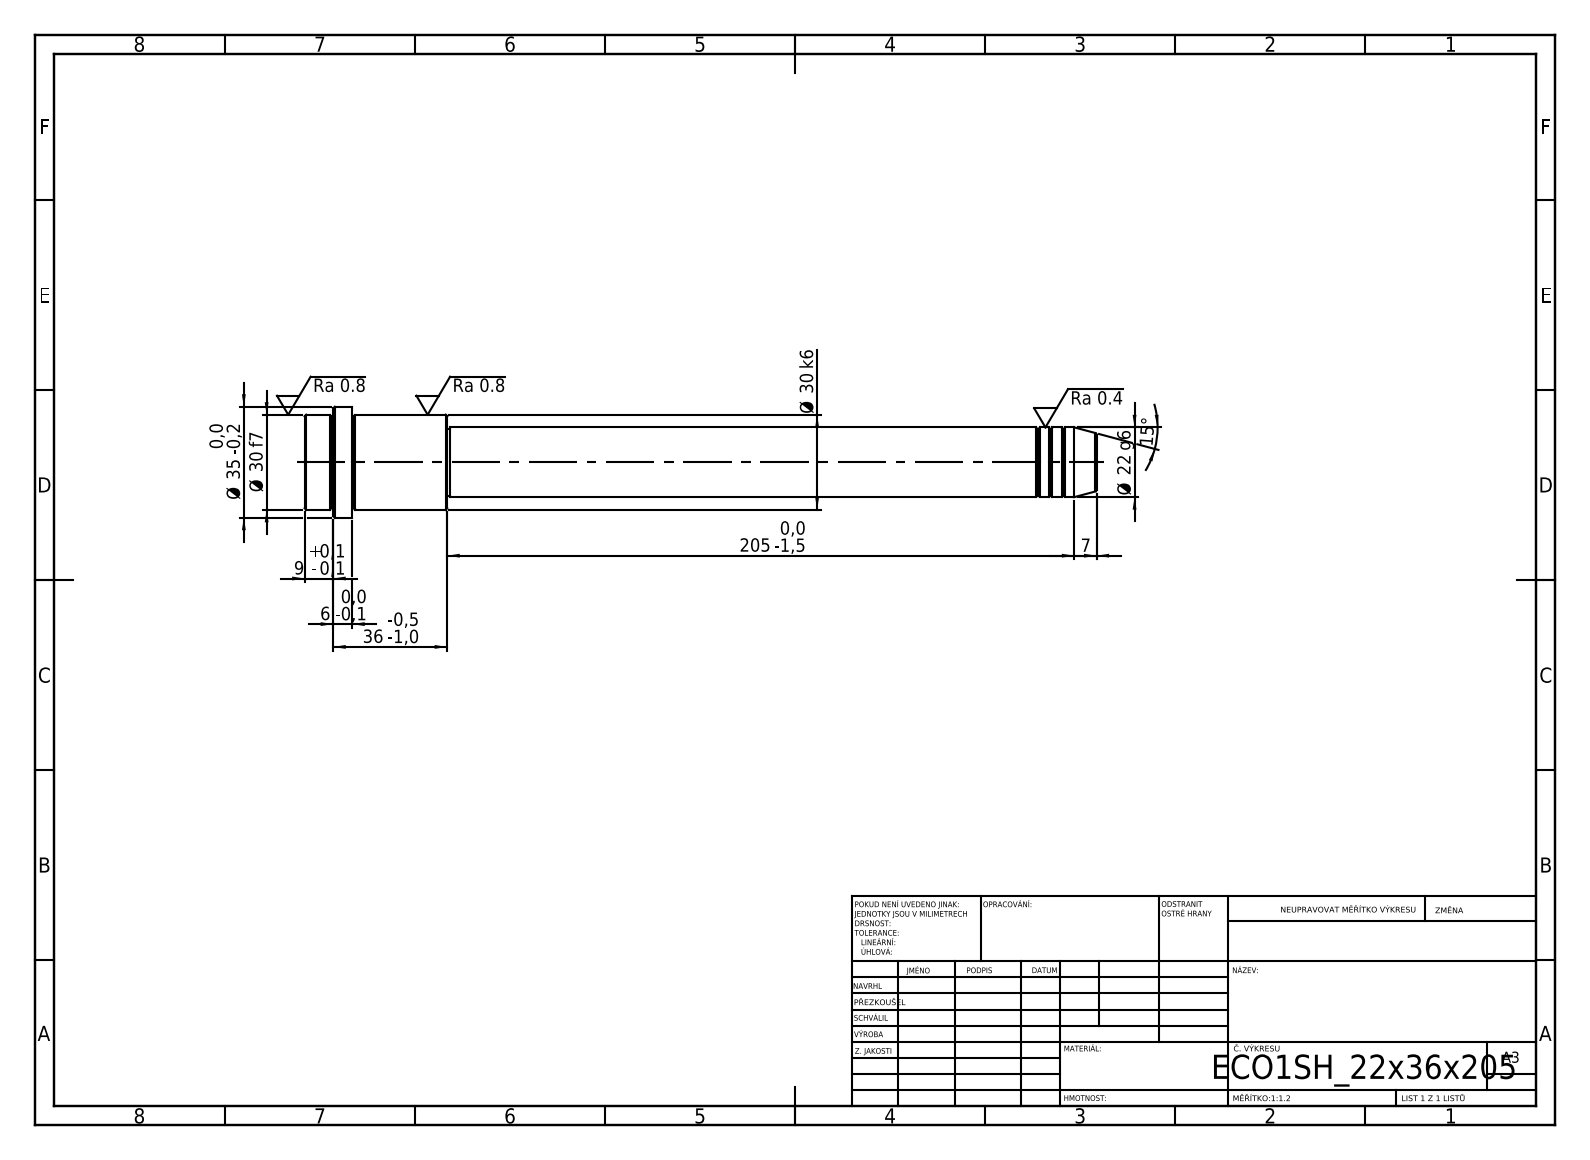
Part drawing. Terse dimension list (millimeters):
written by: SolidWorks 2019 (CONFIG_CONTROL_DESIGN)
unit: mm
bodies: 1 solid, 52 faces (6 planar, 16 cylindrical, 30 other)
size: 250 × 35 × 35
volume: 110 614 mm³; area: 20 464 mm²
bosses: 1× ⌀35, 1× ⌀30, 1× ⌀22, 1× ⌀21
face distances: 45, 30, 15, 205, 235, 250, 241, 36, 6, 9
